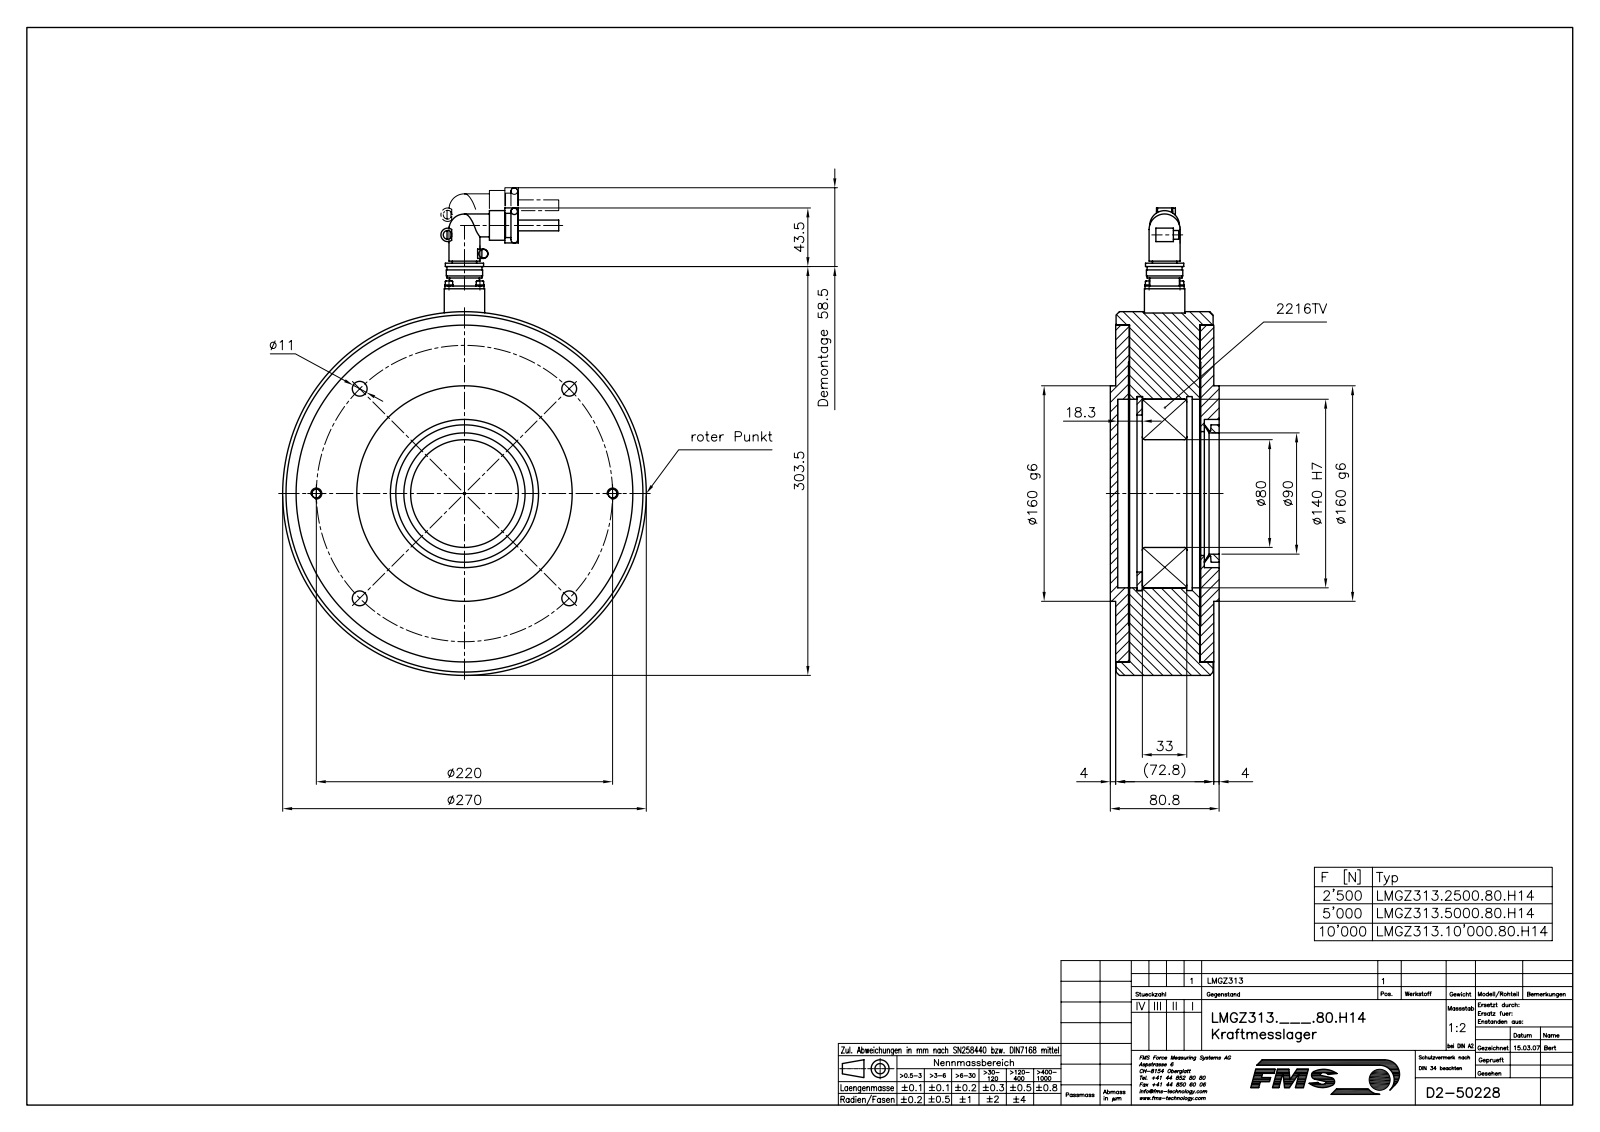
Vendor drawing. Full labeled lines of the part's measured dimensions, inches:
Part name (STEP PRODUCT): L50228; L4899004; TEIL1; L49342 (+8 more)
STEP written by: Mechanical Desktop 2007 (CONFIG_CONTROL_DESIGN)
Units: inches
Bodies: 20 solids, 386 faces (111 planar, 222 cylindrical, 53 other)
Overall size (bounding box): 13.661 × 12.61 × 10.63
Volume: 220.1 in³ · Surface area: 886.9 in²
Round holes (diameter × count): ⌀0.102 ×4, ⌀0.126 ×4, ⌀0.134 ×4, ⌀0.138 ×4, ⌀0.433 ×4, ⌀0.472 ×4, ⌀0.272 ×2, ⌀0.354 ×2, ⌀0.394 ×2, ⌀0.591 ×2, ⌀0.906 ×1, ⌀3.15 ×1
Round bosses / shafts (diameter × count): ⌀0.244 ×4, ⌀0.217 ×4, ⌀0.118 ×4, ⌀0.315 ×3, ⌀0.866 ×2, ⌀0.512 ×2, ⌀0.256 ×2, ⌀0.189 ×2
Partial cylindrical surfaces — rounded edges, fillets, slot ends (radius × count): R0.098 ×2, R0.138 ×1, R0.197 ×1
Main face-to-face distances: 2.059, 0.406, 2.047, 2.079, 0.02, 2.472, 0.394, 2.453, 0.157, 0.374
Hole centre spacings: 4.331, 0.64, 0.906, 3.315, 6.124, 8.002, 8.661, 1.281
